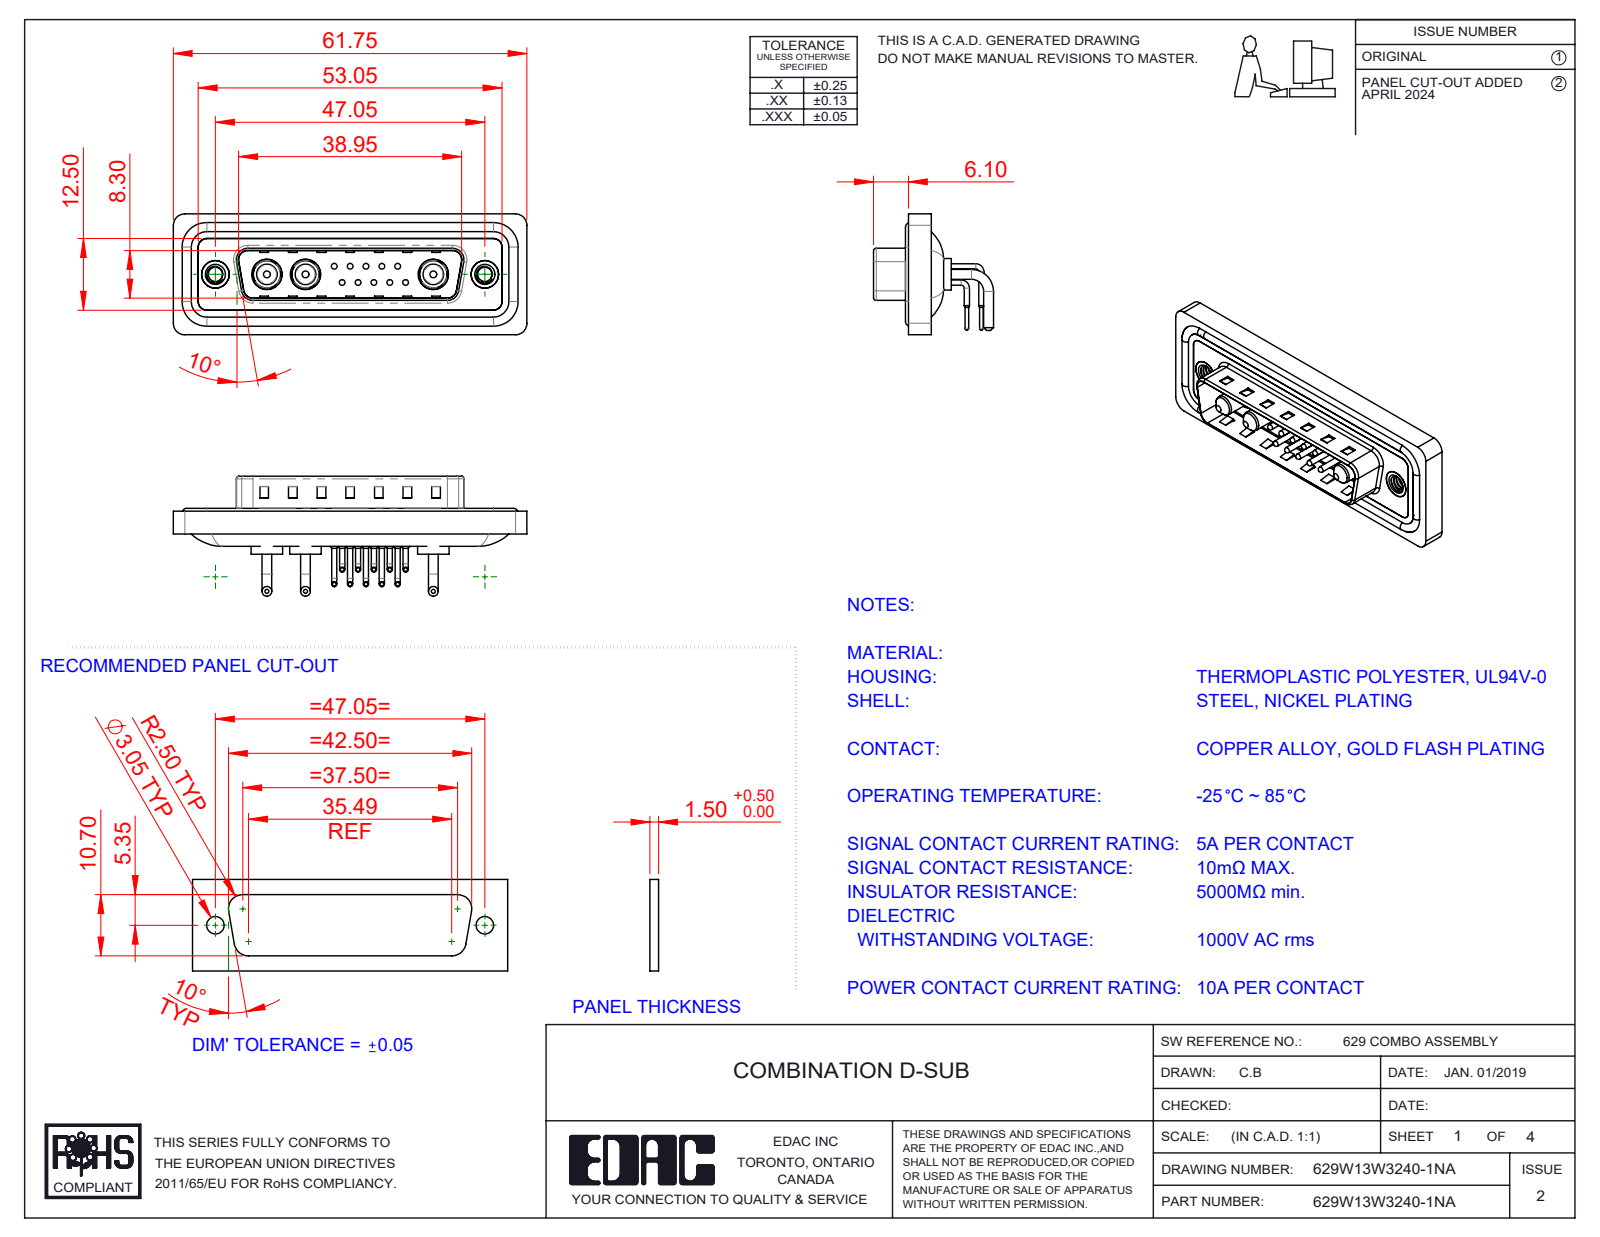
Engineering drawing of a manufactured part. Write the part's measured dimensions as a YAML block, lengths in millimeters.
part_name: "629Combo Shell Front_25 Contacts; 629Combo Housing_13W3; Power Pin_10A RA; 629Combo Waterproof Housing_25 Contacts (+5 more)"
step_written_by: "SolidWorks 2023 (CONFIG_CONTROL_DESIGN)"
units: millimeters
bodies: {solids: 23, faces: 1706, planar: 879, cylindrical: 609, other: 218}
overall_size: [61.75, 21.1, 20.95]
volume: 7440
surface_area: 12347
round_holes:
  - {diameter: 0.75, count: 10}
  - {diameter: 1.6, count: 10}
  - {diameter: 2, count: 10}
  - {diameter: 4.85, count: 3}
  - {diameter: 5.3, count: 3}
  - {diameter: 2.5, count: 2}
  - {diameter: 4, count: 2}
  - {diameter: 4.8, count: 2}
  - {diameter: 5, count: 2}
round_bosses_or_shafts:
  - {diameter: 0.9, count: 20}
  - {diameter: 1.5, count: 10}
  - {diameter: 1, count: 10}
  - {diameter: 0.65, count: 10}
  - {diameter: 1.7, count: 6}
  - {diameter: 1.6, count: 4}
  - {diameter: 5.5, count: 3}
  - {diameter: 5.2, count: 3}
partial_cylinders:
  - {radius: 1.5, count: 18}
  - {radius: 2, count: 18}
  - {radius: 1.01, count: 10}
  - {radius: 0.5, count: 8}
  - {radius: 1.6, count: 8}
  - {radius: 0.25, count: 4}
  - {radius: 0.6, count: 4}
  - {radius: 0.65, count: 4}
face_to_face_distances: [0.4, 2.9, 0.8, 4.1, 1.1, 2.1, 1.6, 4.5, 1.5, 6]
hole_center_spacings: [3.16, 2.77, 5.04, 5.54, 7.49, 5.03, 8.31, 10.11]
